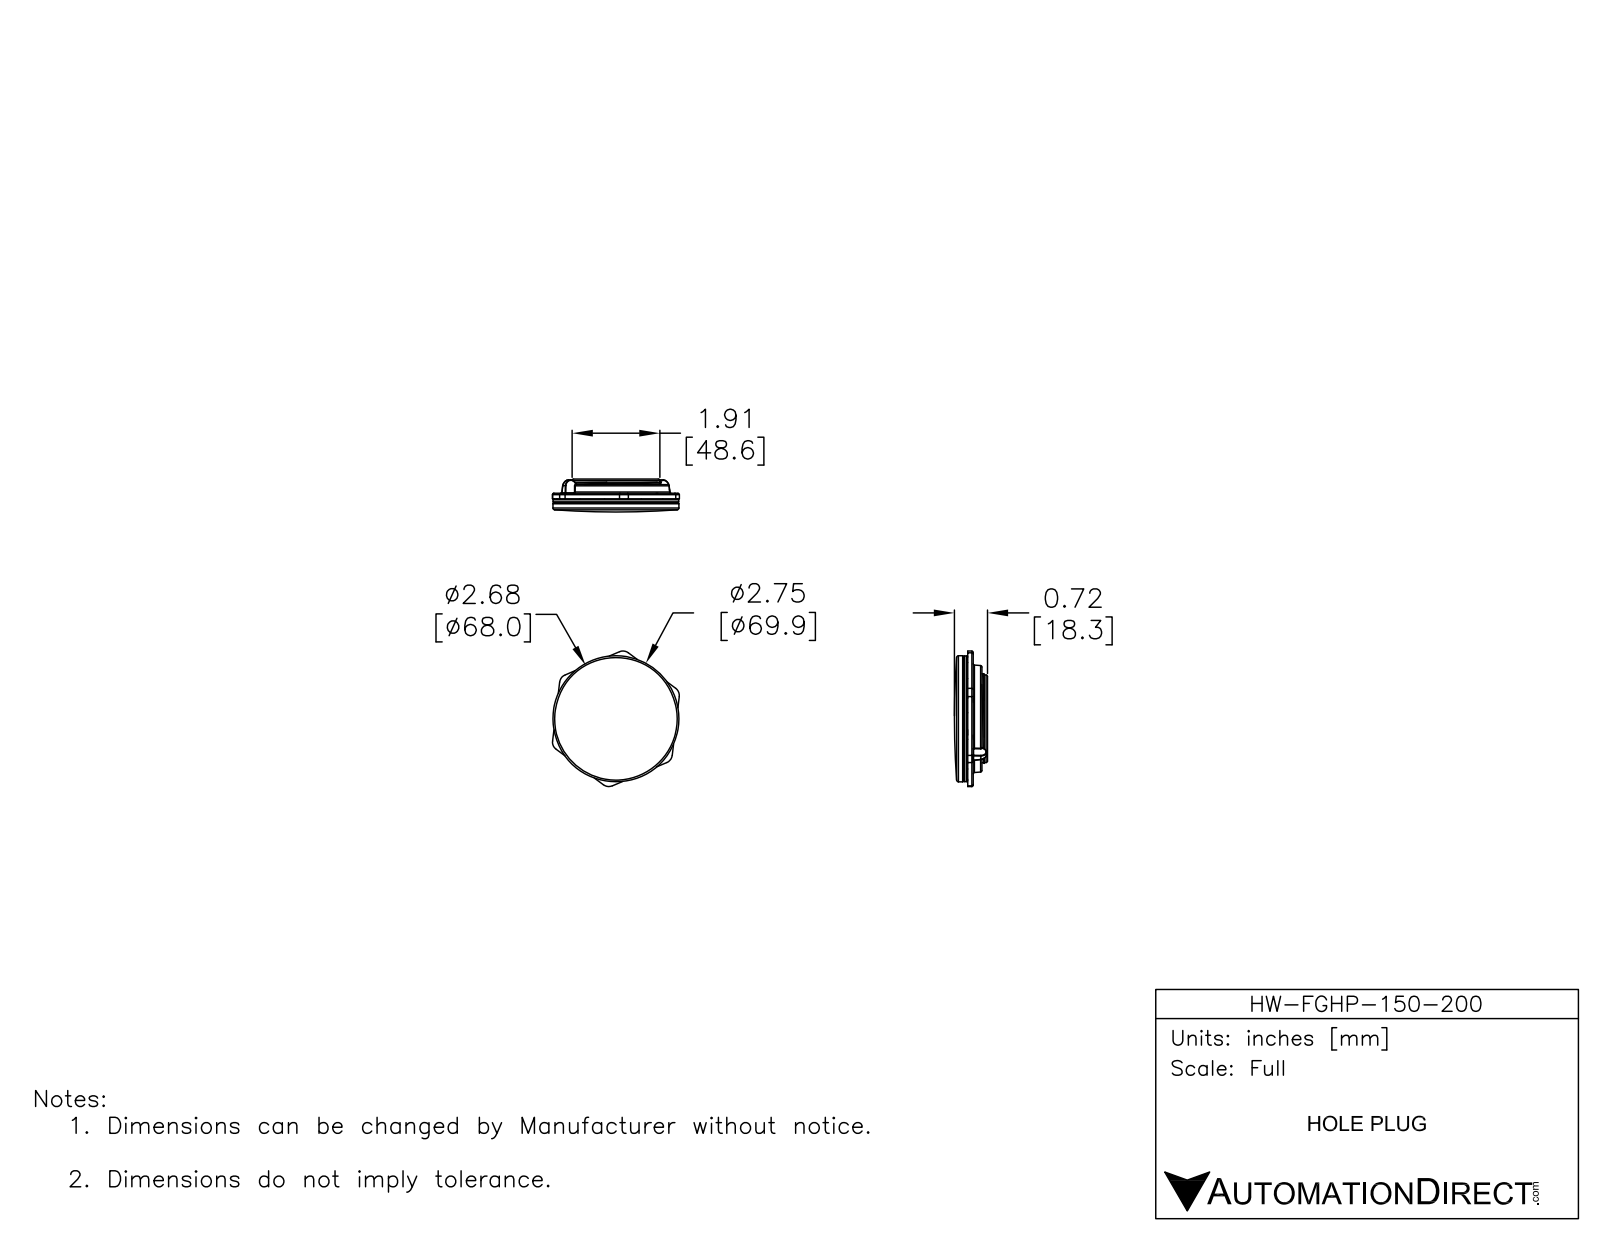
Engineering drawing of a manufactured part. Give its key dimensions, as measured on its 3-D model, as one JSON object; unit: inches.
{"part_name": "HP9; HP9_1; HP9_2; HPSERIES4_STP", "step_written_by": "Autodesk Inventor 2014 (AUTOMOTIVE_DESIGN)", "units": "inches", "bodies": {"solids": 3, "faces": 151, "planar": 32, "cylindrical": 53, "other": 66}, "overall_size": [2.957, 2.769, 0.72], "volume_in3": 2.682, "surface_area_in2": 35.83, "round_holes": [[1.97, 1]], "round_bosses_or_shafts": [[2.75, 1], [2.74, 1], [1.91, 1]], "partial_cylinders_radius": [[0.03, 14], [0.009, 8], [0.08, 8], [0.01, 6], [0.196, 6], [0.154, 2], [0.018, 1]], "face_to_face_distances": [0.099, 0.089, 0.431, 0.52, 0.53, 0.311, 0.12, 0.209, 0.219, 0.121]}
